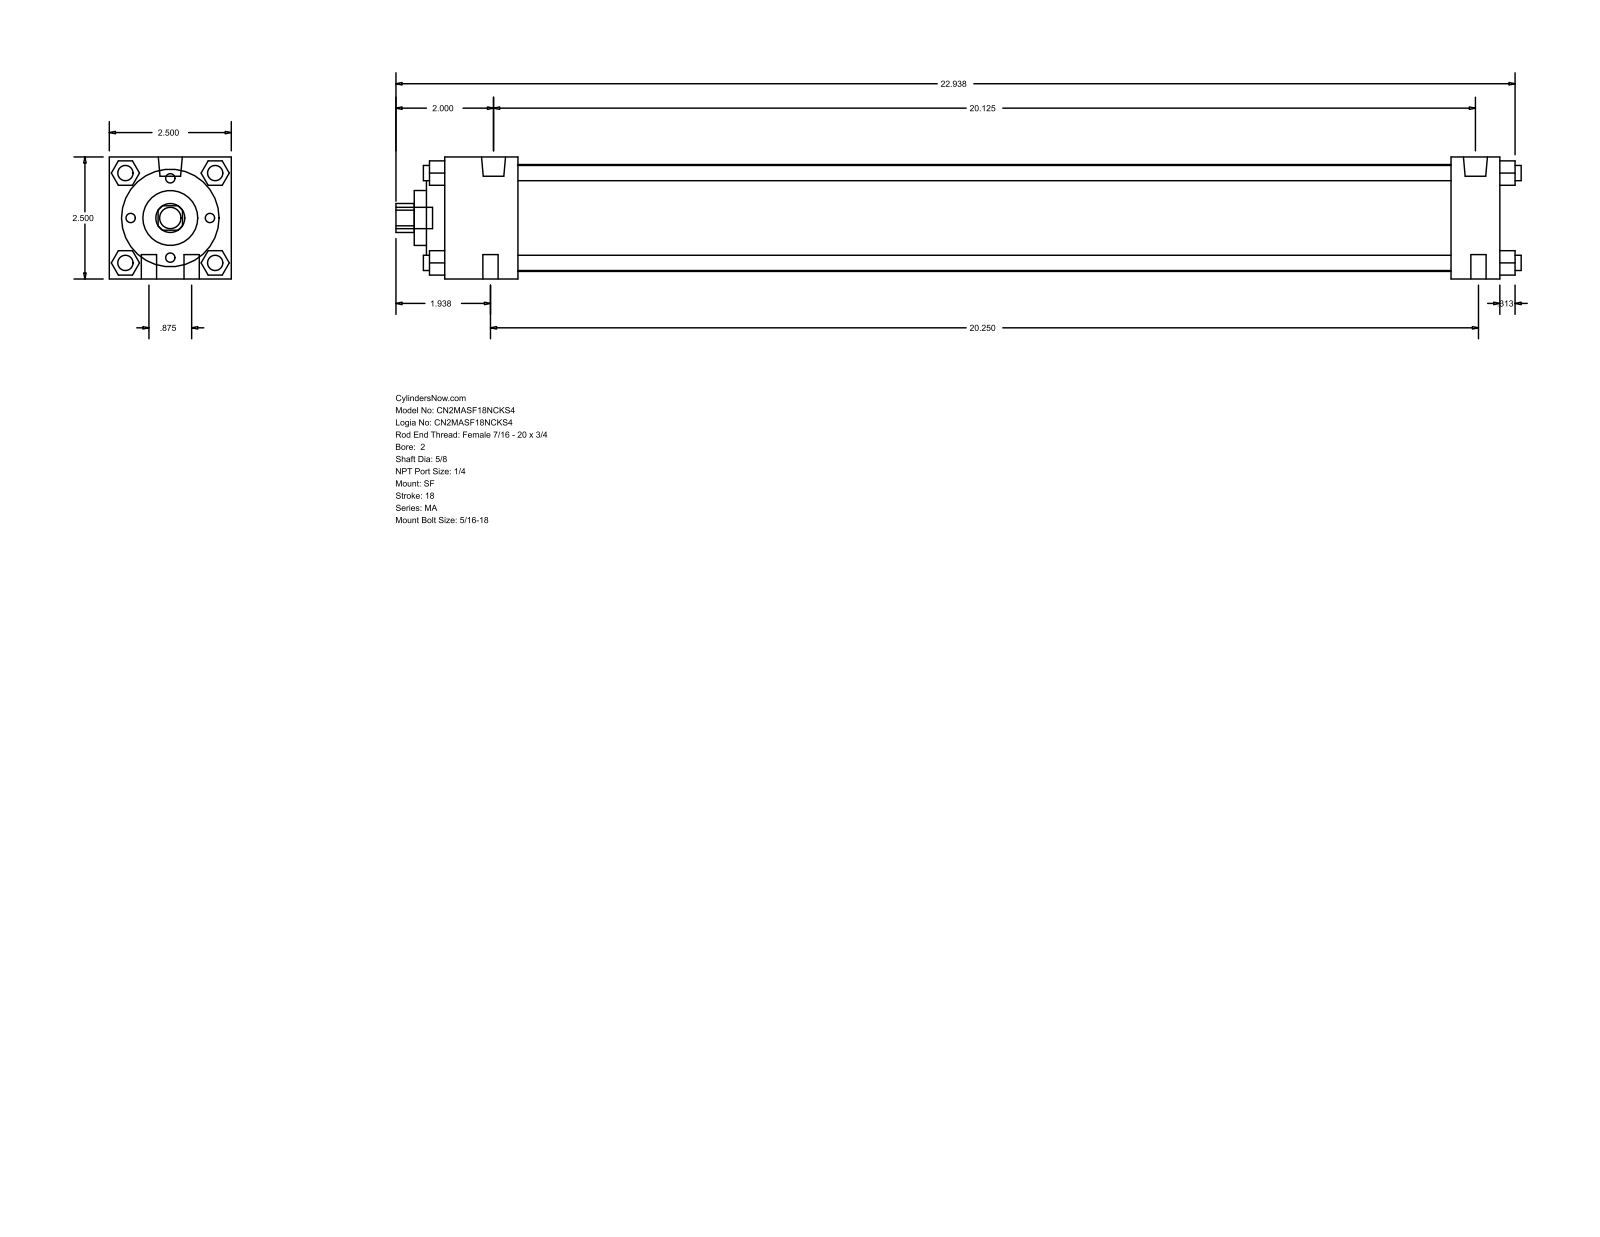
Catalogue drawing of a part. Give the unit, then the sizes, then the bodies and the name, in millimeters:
Units: millimetres
Overall size (bounding box): 585.79 × 63.5 × 63.5
Round holes (diameter × count): ⌀15.88 ×1, ⌀28.57 ×1, ⌀50.8 ×1, ⌀55.63 ×1
Round bosses / shafts (diameter × count): ⌀7.94 ×10, ⌀12.49 ×2, ⌀11.11 ×1
Partial cylindrical surfaces — rounded edges, fillets, slot ends (radius × count): R7.54 ×1
Main face-to-face distances: 63.5, 12.7, 25.4, 38.1, 549.27, 9.52, 523.87, 485.77, 511.17, 47.62
Bodies: 0 solids, 126 faces (95 planar, 31 cylindrical, 0 other)
Part name (STEP PRODUCT): MA_SF__0200_0.625
STEP written by: GSSL Pune (CONFIG_CONTROL_DESIGN)
